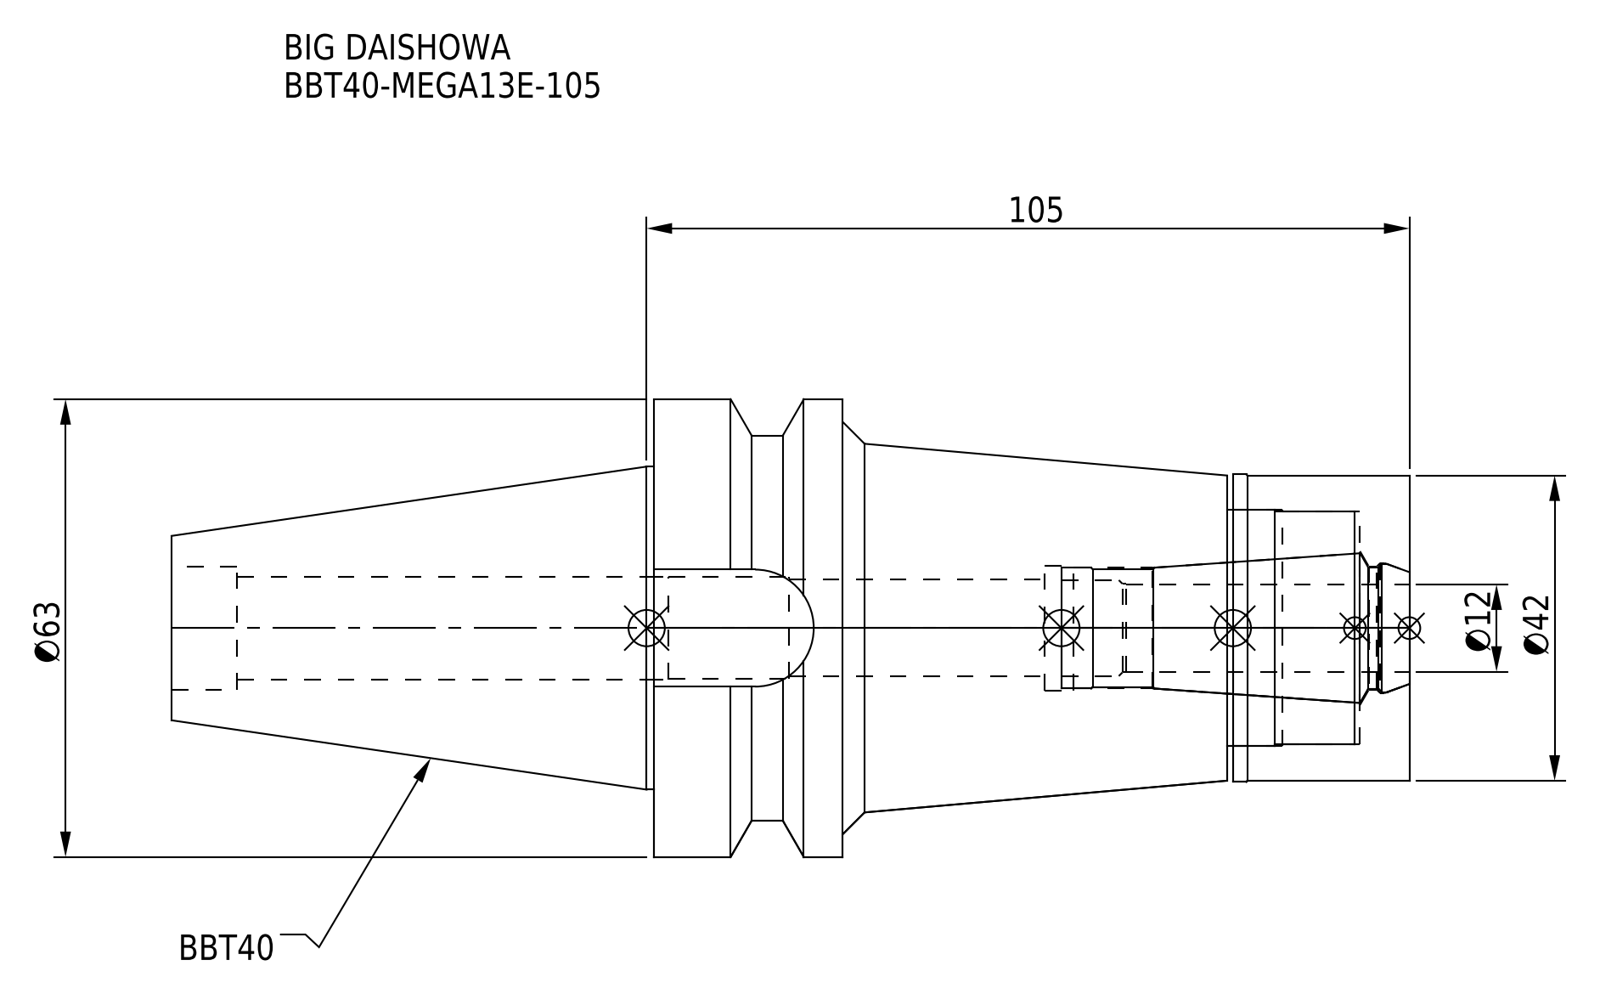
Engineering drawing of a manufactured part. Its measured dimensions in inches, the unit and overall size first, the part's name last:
Units: inches
Overall size (bounding box): 6.709 × 2.48 × 2.48
Round holes (diameter × count): ⌀0.524 ×1, ⌀0.551 ×1, ⌀0.559 ×1, ⌀0.654 ×1, ⌀0.669 ×1, ⌀0.677 ×1, ⌀0.705 ×1, ⌀1.26 ×1, ⌀1.28 ×1
Round bosses / shafts (diameter × count): ⌀2.48 ×1, ⌀2.087 ×1, ⌀1.75 ×1, ⌀1.665 ×1, ⌀1.654 ×1
Partial cylindrical surfaces — rounded edges, fillets, slot ends (radius × count): R0.317 ×1
Main face-to-face distances: 4.094, 0.988, 3.071, 1.024, 0.957, 2.114, 3.138, 0.031, 2.083, 3.106
Volume: 13.99 in³ · Surface area: 65.94 in²
Bodies: 2 solids, 81 faces (21 planar, 40 cylindrical, 20 other)
Part name (STEP PRODUCT): MEN13_1.stp; BBT40-MEGA13E-105-120-FreeParts; BBT40-MEGA13E-105; BBT40-MEGA13E-105_1.stp (+3 more)
STEP written by: SolidWorks 2019 (CONFIG_CONTROL_DESIGN)
